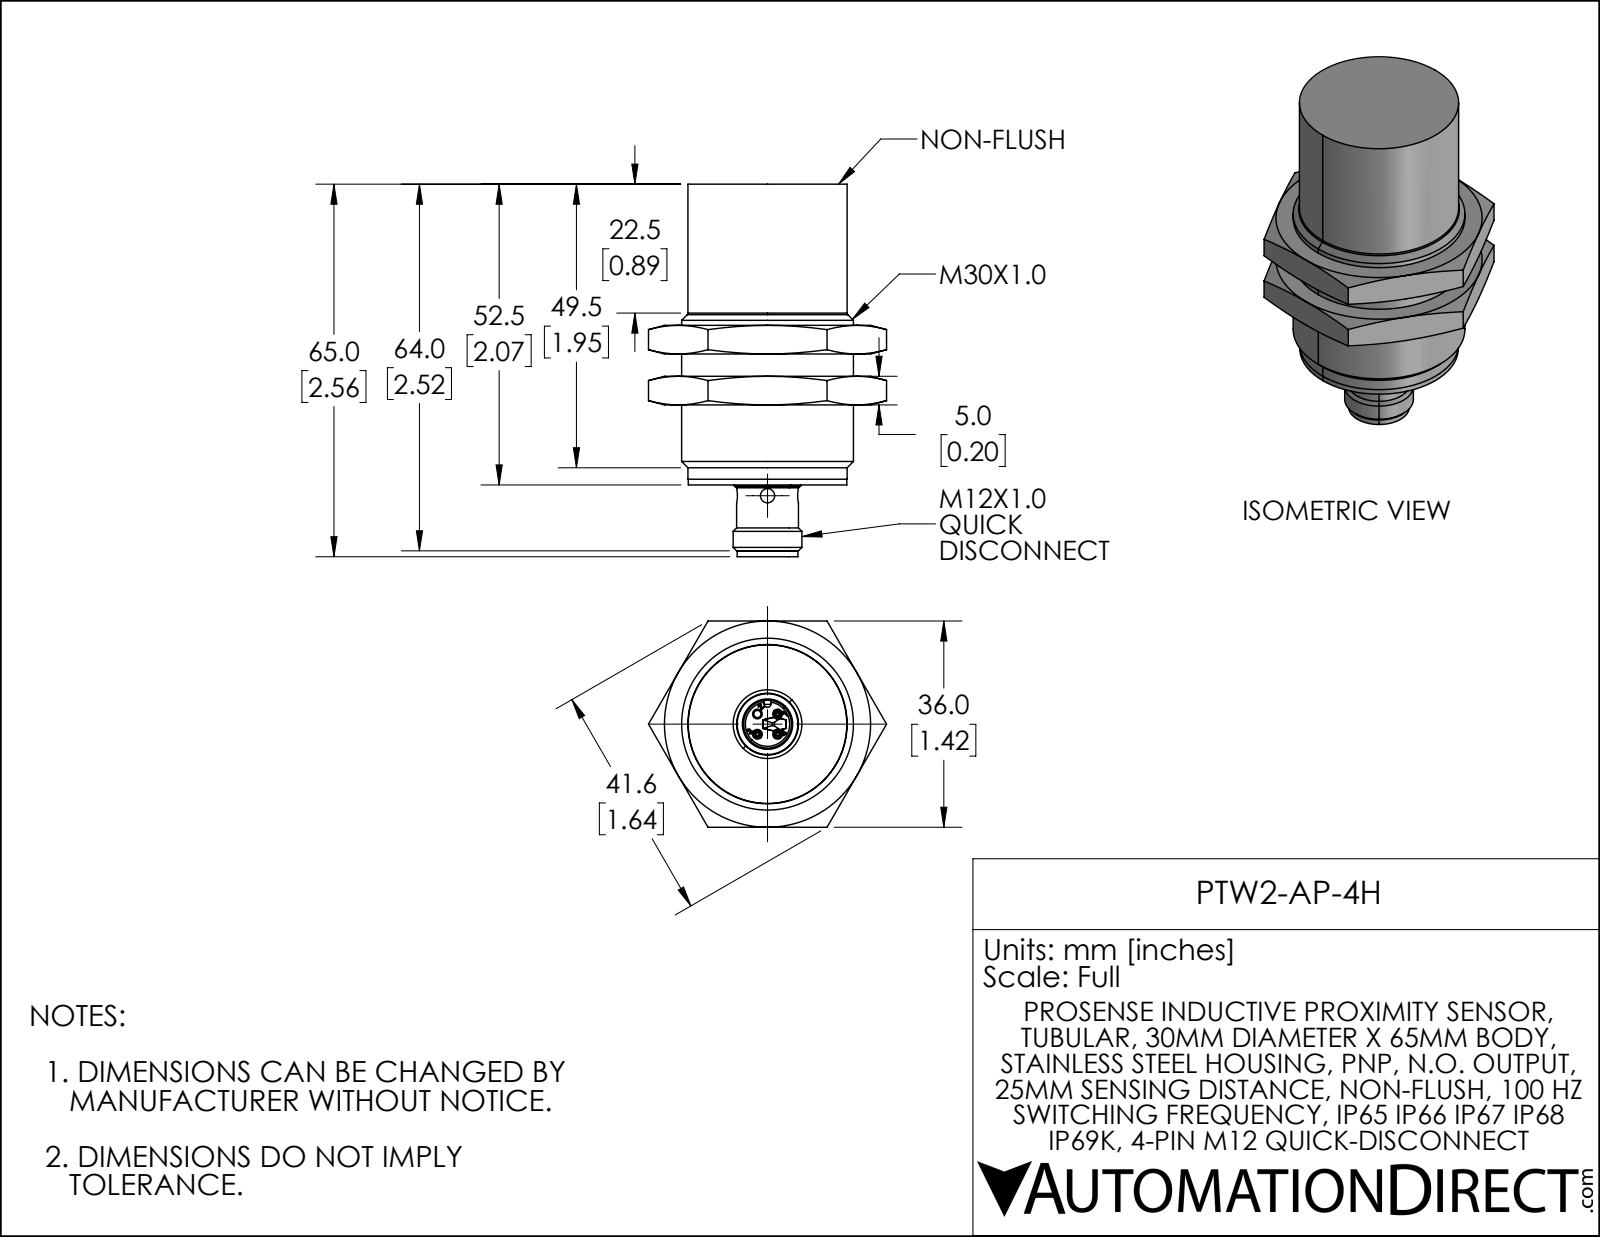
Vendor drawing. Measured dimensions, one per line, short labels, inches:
name: PTW2-AP-4H
written by: SolidWorks 2019 (AUTOMOTIVE_DESIGN)
unit: in
bodies: 3 solids, 413 faces (106 planar, 111 cylindrical, 196 other)
size: 2.56 × 1.637 × 1.417
volume: 2.43 in³; area: 18.35 in²
holes: 3× ⌀0.041, 3× ⌀0.043, 2× ⌀0.098, 1× ⌀0.329, 1× ⌀0.394, 1× ⌀1.071, 1× ⌀1.117
bosses: 3× ⌀0.039, 1× ⌀1.181, 1× ⌀1.094, 1× ⌀1.09, 1× ⌀1.07, 1× ⌀0.472, 1× ⌀0.457, 1× ⌀0.425
rounds: 18× R0.012, 3× R0.02, 2× R0.02, 1× R0.02, 1× R0.021, 1× R0.024, 1× R0.16, 1× R0.161
face distances: 0.35, 0.197, 1.417, 2.067, 0.97, 1.097, 1.32, 0.747, 1.167, 0.153
hole spacings: 0.098, 0.139, 0.197
